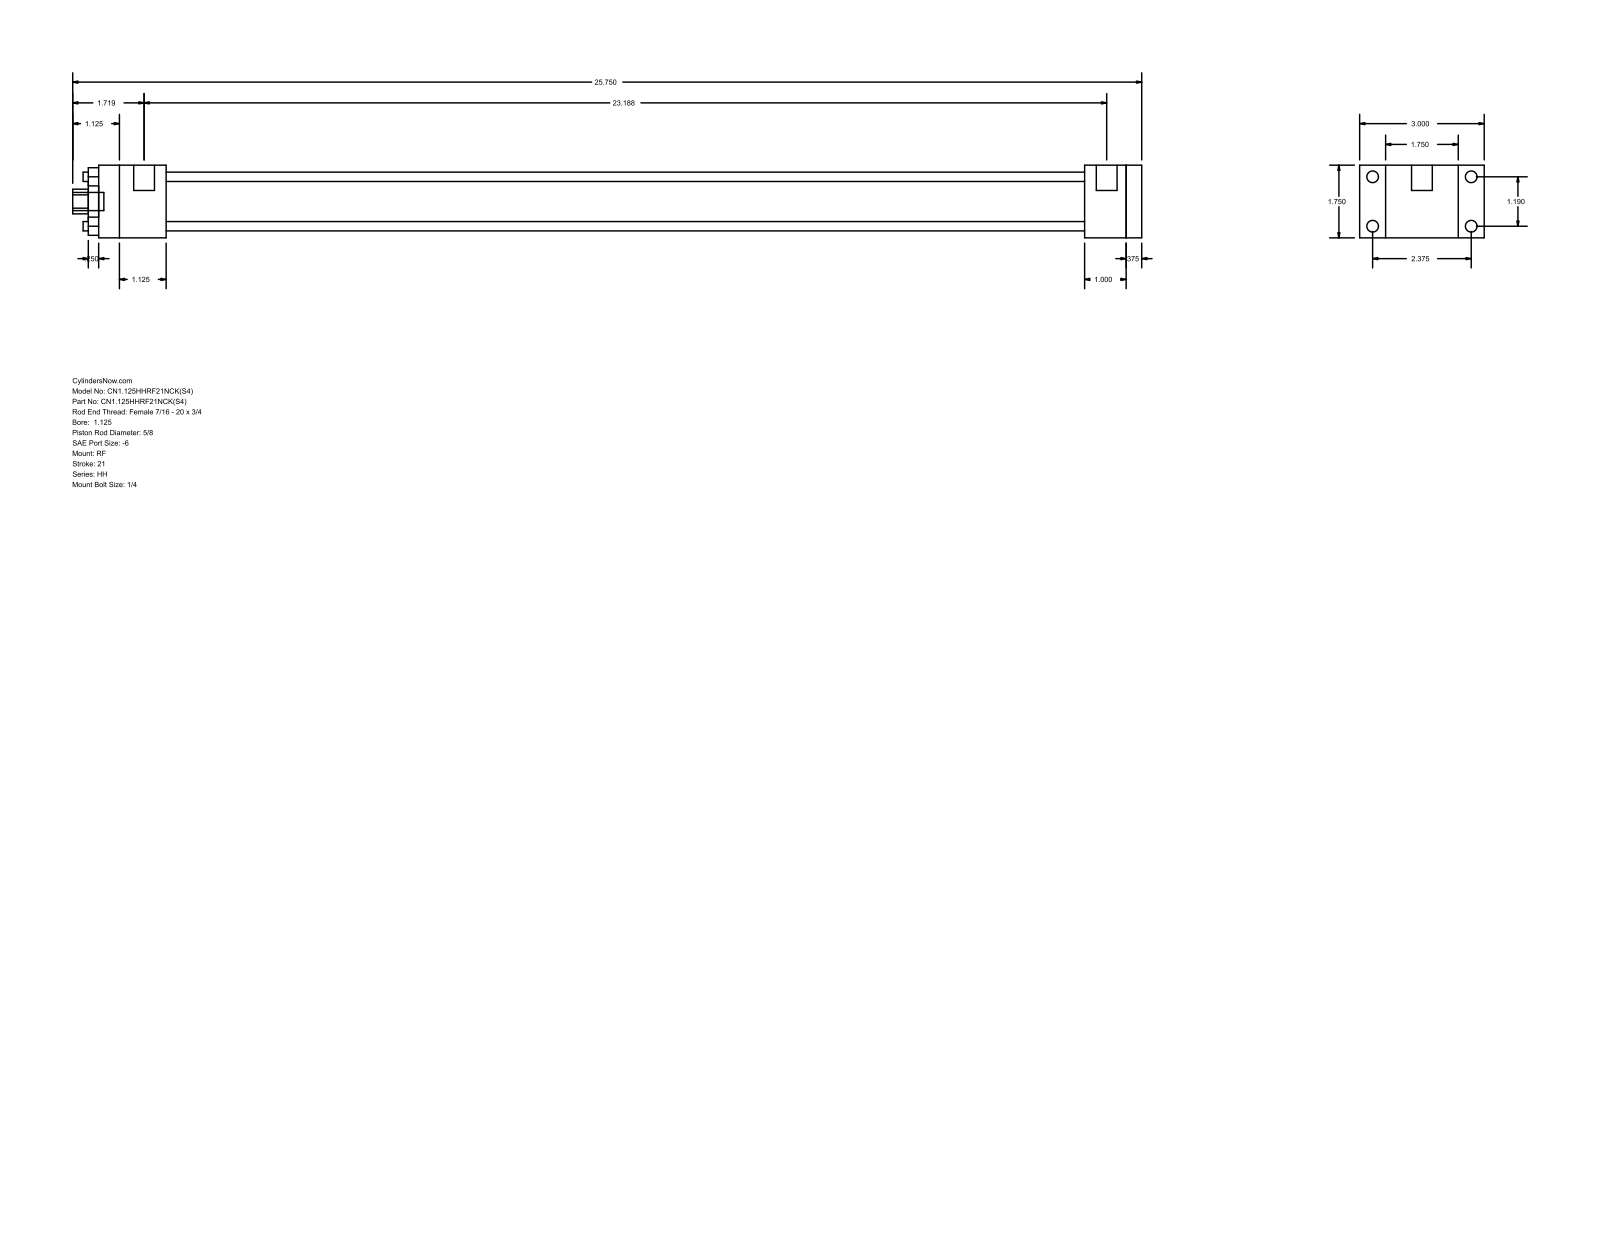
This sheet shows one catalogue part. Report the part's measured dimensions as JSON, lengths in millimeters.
{"part_name": "HH_RF__0112_0.625", "step_written_by": "GSSL Pune (CONFIG_CONTROL_DESIGN)", "units": "millimeters", "bodies": {"solids": 0, "faces": 92, "planar": 64, "cylindrical": 28, "other": 0}, "overall_size": [654.05, 76.2, 44.45], "round_holes": [[5.71, 4], [15.88, 1], [28.57, 1], [34.92, 1]], "round_bosses_or_shafts": [[7.14, 4], [5.56, 4], [12.7, 2], [11.11, 1]], "partial_cylinders_radius": [[7.54, 1]], "face_to_face_distances": [44.46, 9.53, 638.17, 15.87, 587.37, 596.9, 561.97, 25.4, 34.93, 41.27], "hole_center_spacings": [21.37, 30.22, 42.74]}
